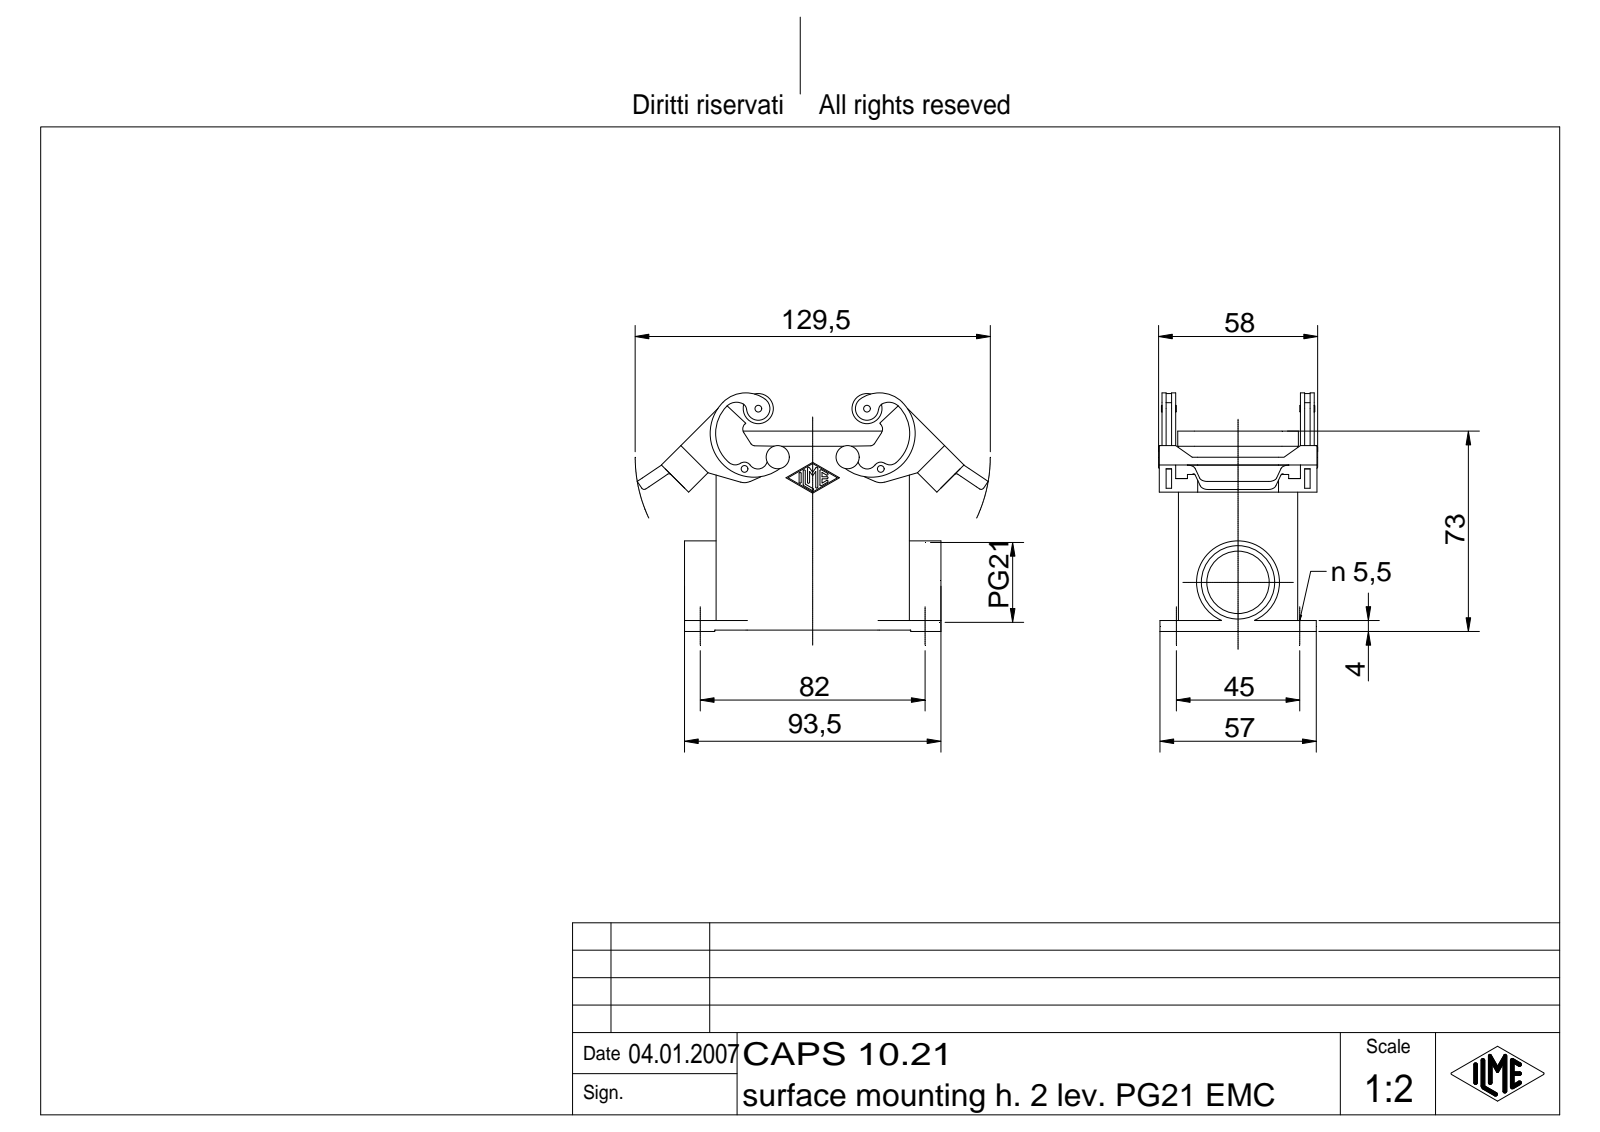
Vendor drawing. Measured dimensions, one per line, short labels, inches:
name: CAP 16 CP29
written by: Autodesk Inventor 7 (AUTOMOTIVE_DESIGN)
unit: in
bodies: 2 solids, 475 faces (175 planar, 179 cylindrical, 121 other)
size: 5.256 × 4.606 × 3.002
volume: 7.874 in³; area: 115.4 in²
holes: 4× ⌀0.217, 1× ⌀0.157, 1× ⌀0.197, 1× ⌀1.239, 1× ⌀1.397
bosses: 2× ⌀0.197, 2× ⌀0.118, 1× ⌀1.535, 1× ⌀0.276, 1× ⌀0.157
rounds: 26× R0.039, 14× R0.015, 12× R0.236, 9× R0.02, 8× R0.028, 8× R0.079, 4× R0.118, 4× R0.138
face distances: 0.118, 1.594, 0.138, 1.713, 1.476, 1.142, 0.886, 2.736, 2.618, 1.024
hole spacings: 1.772, 4.134, 4.498
